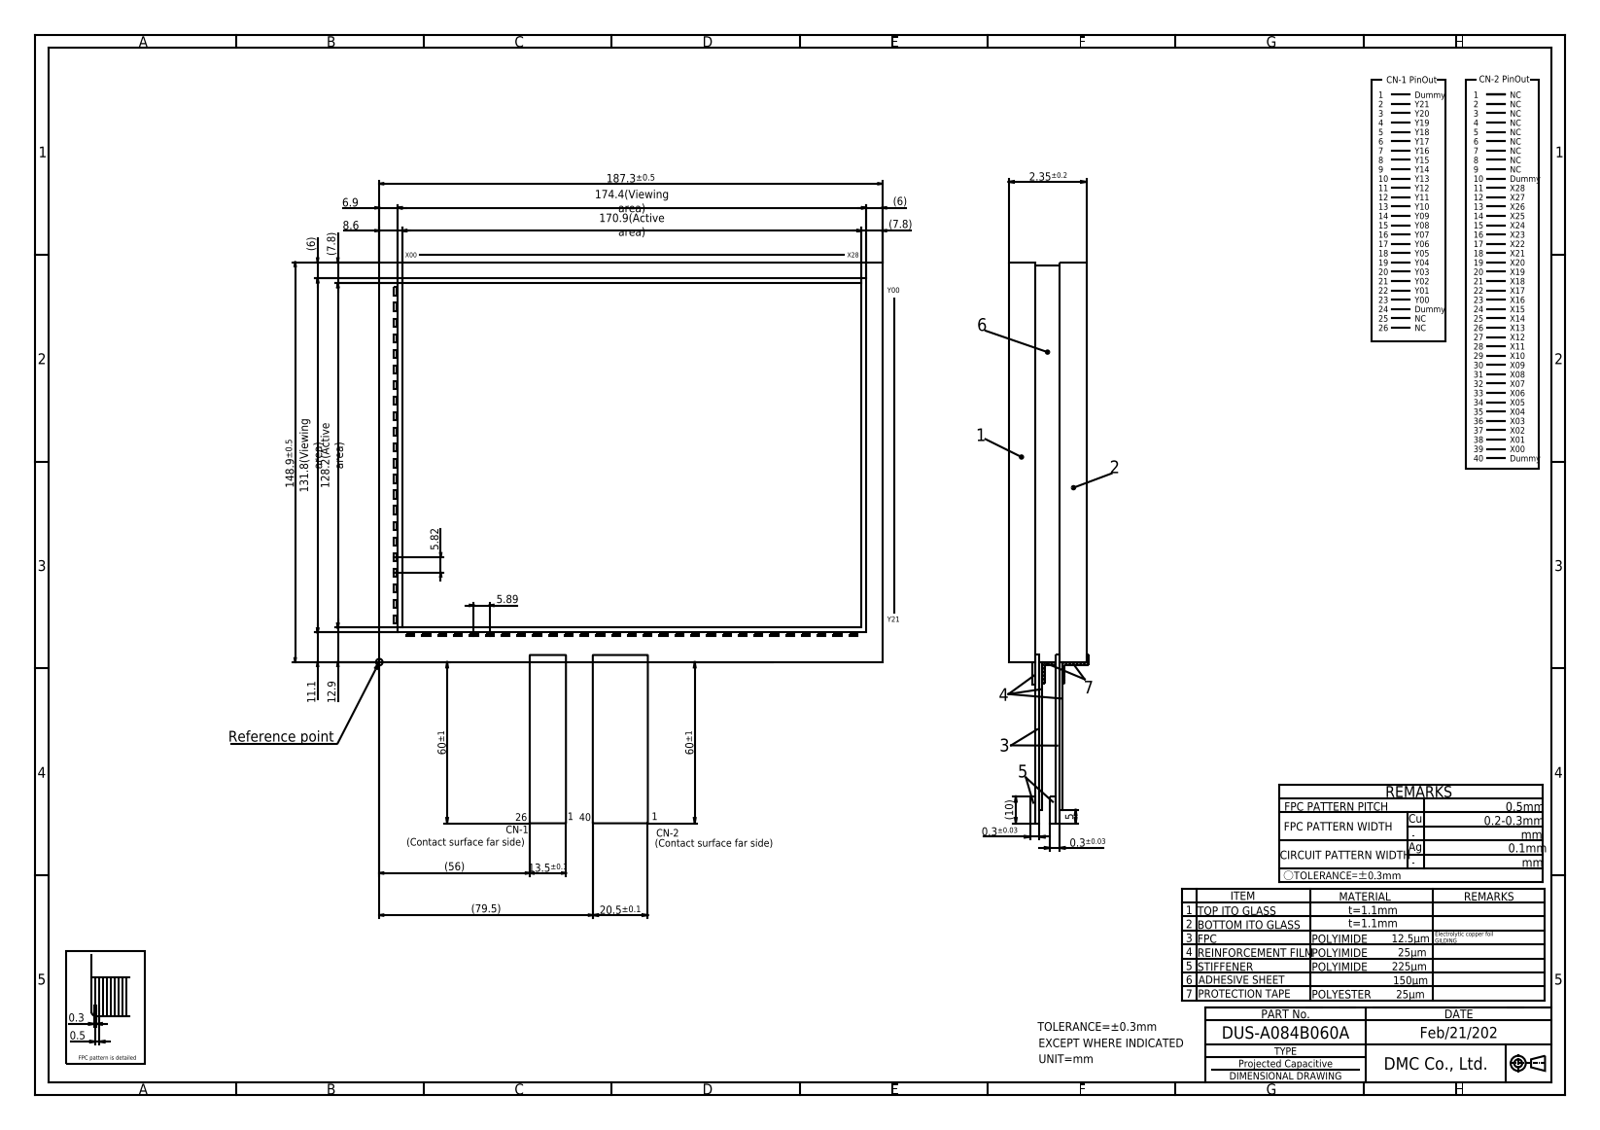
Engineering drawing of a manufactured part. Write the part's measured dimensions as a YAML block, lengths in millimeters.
part_name: "DUS-A084B060A"
step_written_by: "Autodesk Inventor 2020 (CONFIG_CONTROL_DESIGN)"
units: millimeters
bodies: {solids: 1, faces: 302, planar: 298, cylindrical: 4, other: 0}
overall_size: [262.22, 238.68, 2.35]
volume: 65720
surface_area: 61620
partial_cylinders:
  - {radius: 0.2, count: 4}
face_to_face_distances: [2.35, 1.1, 1.2, 1.15, 1.25, 1, 2.25, 148.9, 187.3, 0.8]
